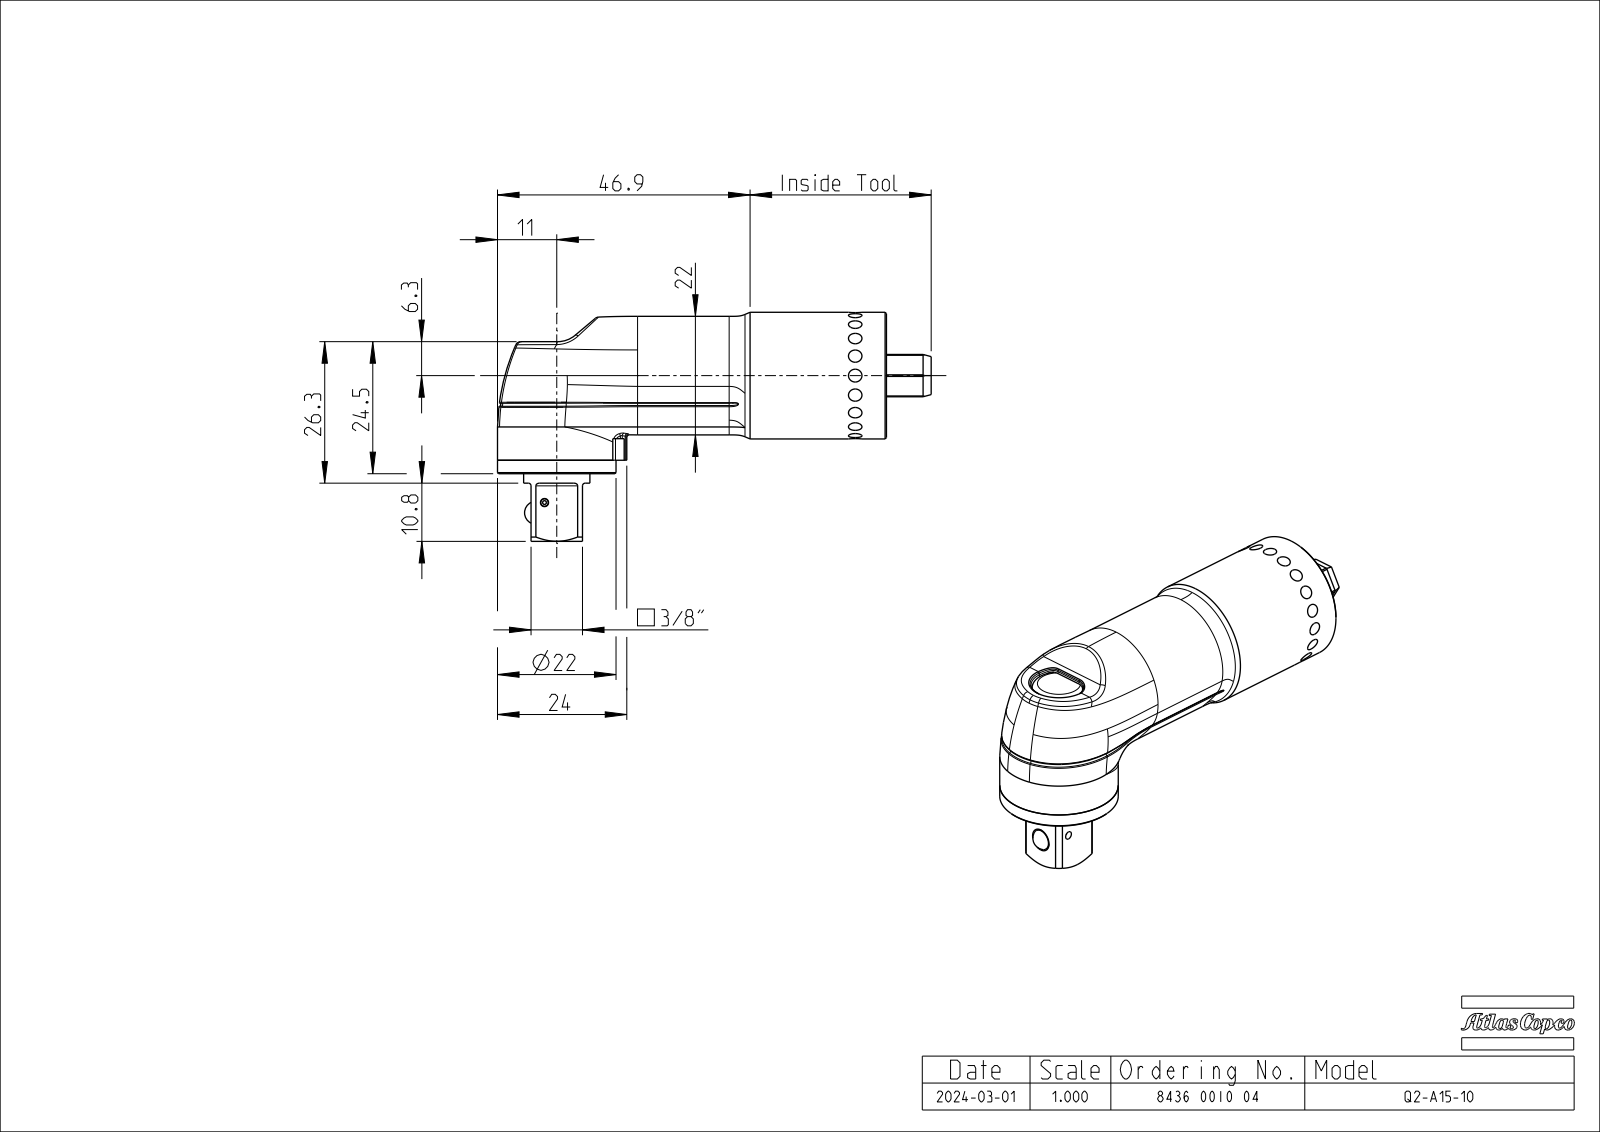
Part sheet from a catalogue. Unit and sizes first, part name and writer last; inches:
Units: inches
Overall size (bounding box): 2.843 × 1.673 × 0.925
Round holes (diameter × count): ⌀0.102 ×4, ⌀0.063 ×1
Round bosses / shafts (diameter × count): ⌀0.925 ×1, ⌀0.866 ×1, ⌀0.484 ×1
Partial cylindrical surfaces — rounded edges, fillets, slot ends (radius × count): R0.02 ×11, R0.008 ×4, R0.012 ×2, R0.197 ×1, R0.433 ×1, R0.466 ×1, R0.512 ×1
Main face-to-face distances: 0.376, 2.221, 0.957, 2.598, 0.494, 1.451, 1.459, 0.965, 0.573, 0.079
Hole centre spacings: 0.346, 0.49, 0.693
Volume: 1.911 in³ · Surface area: 10.55 in²
Bodies: 1 solid, 214 faces (34 planar, 38 cylindrical, 142 other)
Part name (STEP PRODUCT): 4211581280_NOIP
STEP written by: CREO PARAMETRIC BY PTC INC, 2022414 (CONFIG_CONTROL_DESIGN)
